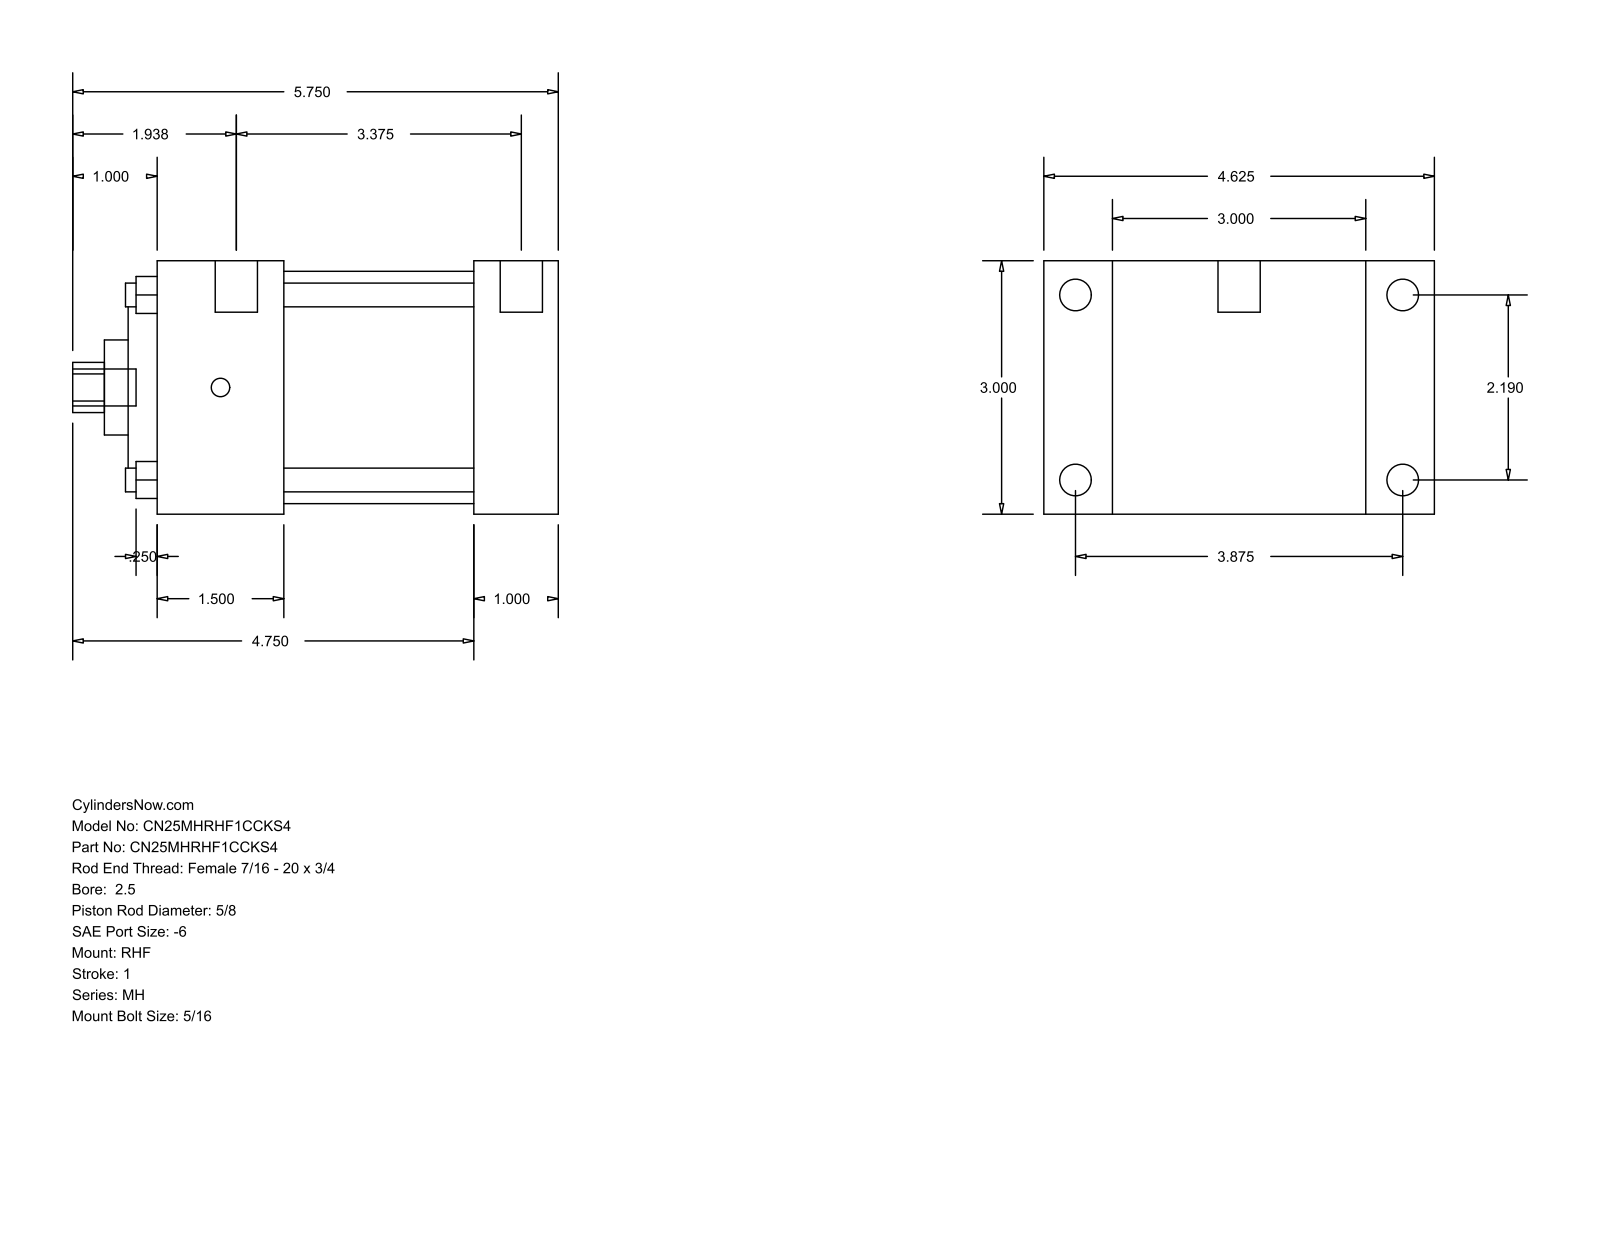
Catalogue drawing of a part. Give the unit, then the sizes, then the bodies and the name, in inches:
Units: inches
Overall size (bounding box): 5.75 × 4.625 × 3
Round holes (diameter × count): ⌀0.281 ×4, ⌀0.625 ×1, ⌀1.125 ×1, ⌀2.187 ×1, ⌀2.75 ×1
Round bosses / shafts (diameter × count): ⌀0.375 ×4, ⌀0.219 ×4, ⌀0.5 ×2, ⌀0.437 ×1
Partial cylindrical surfaces — rounded edges, fillets, slot ends (radius × count): R0.297 ×1
Main face-to-face distances: 3, 1, 0.813, 3.813, 4.75, 3.75, 4.625, 2.25, 1.5, 3.25
Hole centre spacings: 1.548, 2.19, 3.097
Bodies: 0 solids, 90 faces (61 planar, 29 cylindrical, 0 other)
Part name (STEP PRODUCT): MH_RHF__0250_0.625
STEP written by: GSSL Pune (CONFIG_CONTROL_DESIGN)
